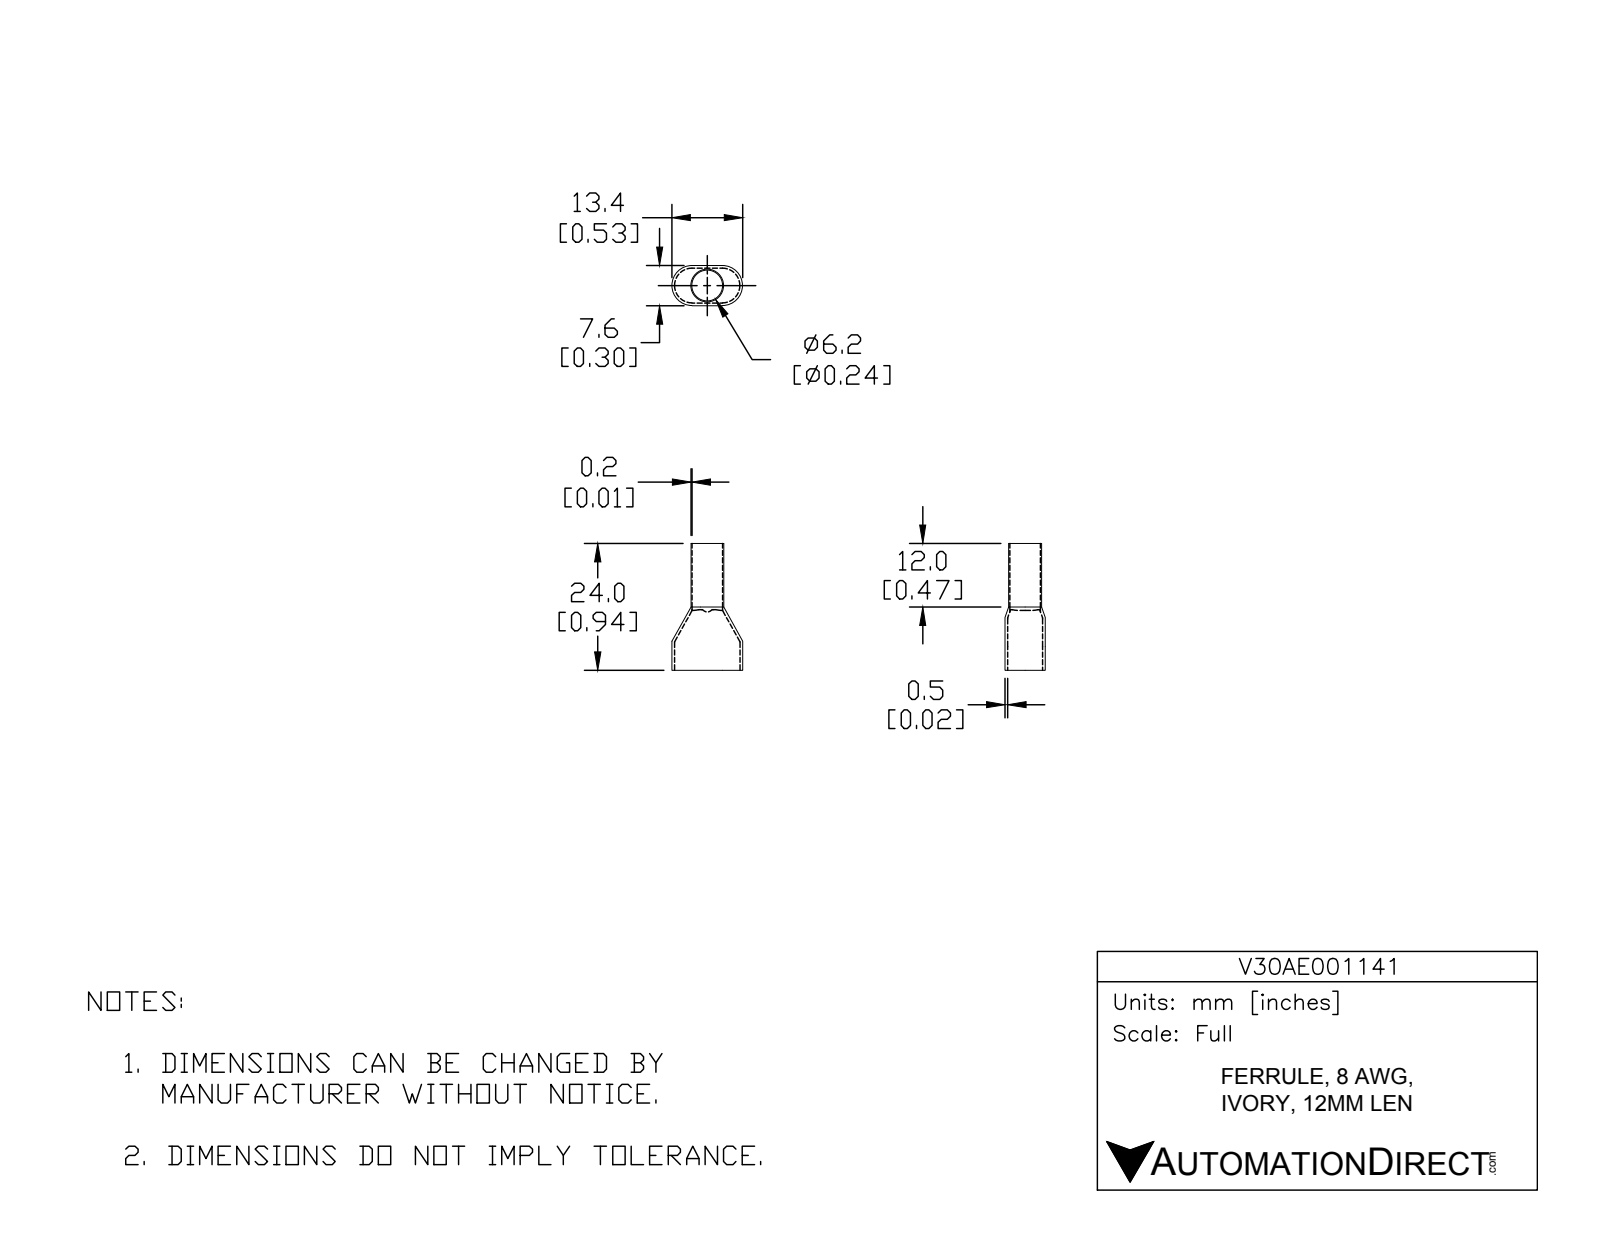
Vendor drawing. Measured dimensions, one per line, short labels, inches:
name: V30AE001141
written by: SolidWorks 2017 (AUTOMOTIVE_DESIGN)
unit: in
bodies: 2 solids, 38 faces (16 planar, 22 cylindrical, 0 other)
size: 0.945 × 0.528 × 0.299
volume: 0.014 in³; area: 1.883 in²
holes: 1× ⌀0.228
bosses: 1× ⌀0.244
rounds: 5× R0.13, 5× R0.15
face distances: 0.02, 0.28, 0.299, 0.26, 0.472, 0.945, 0.453, 0.492
